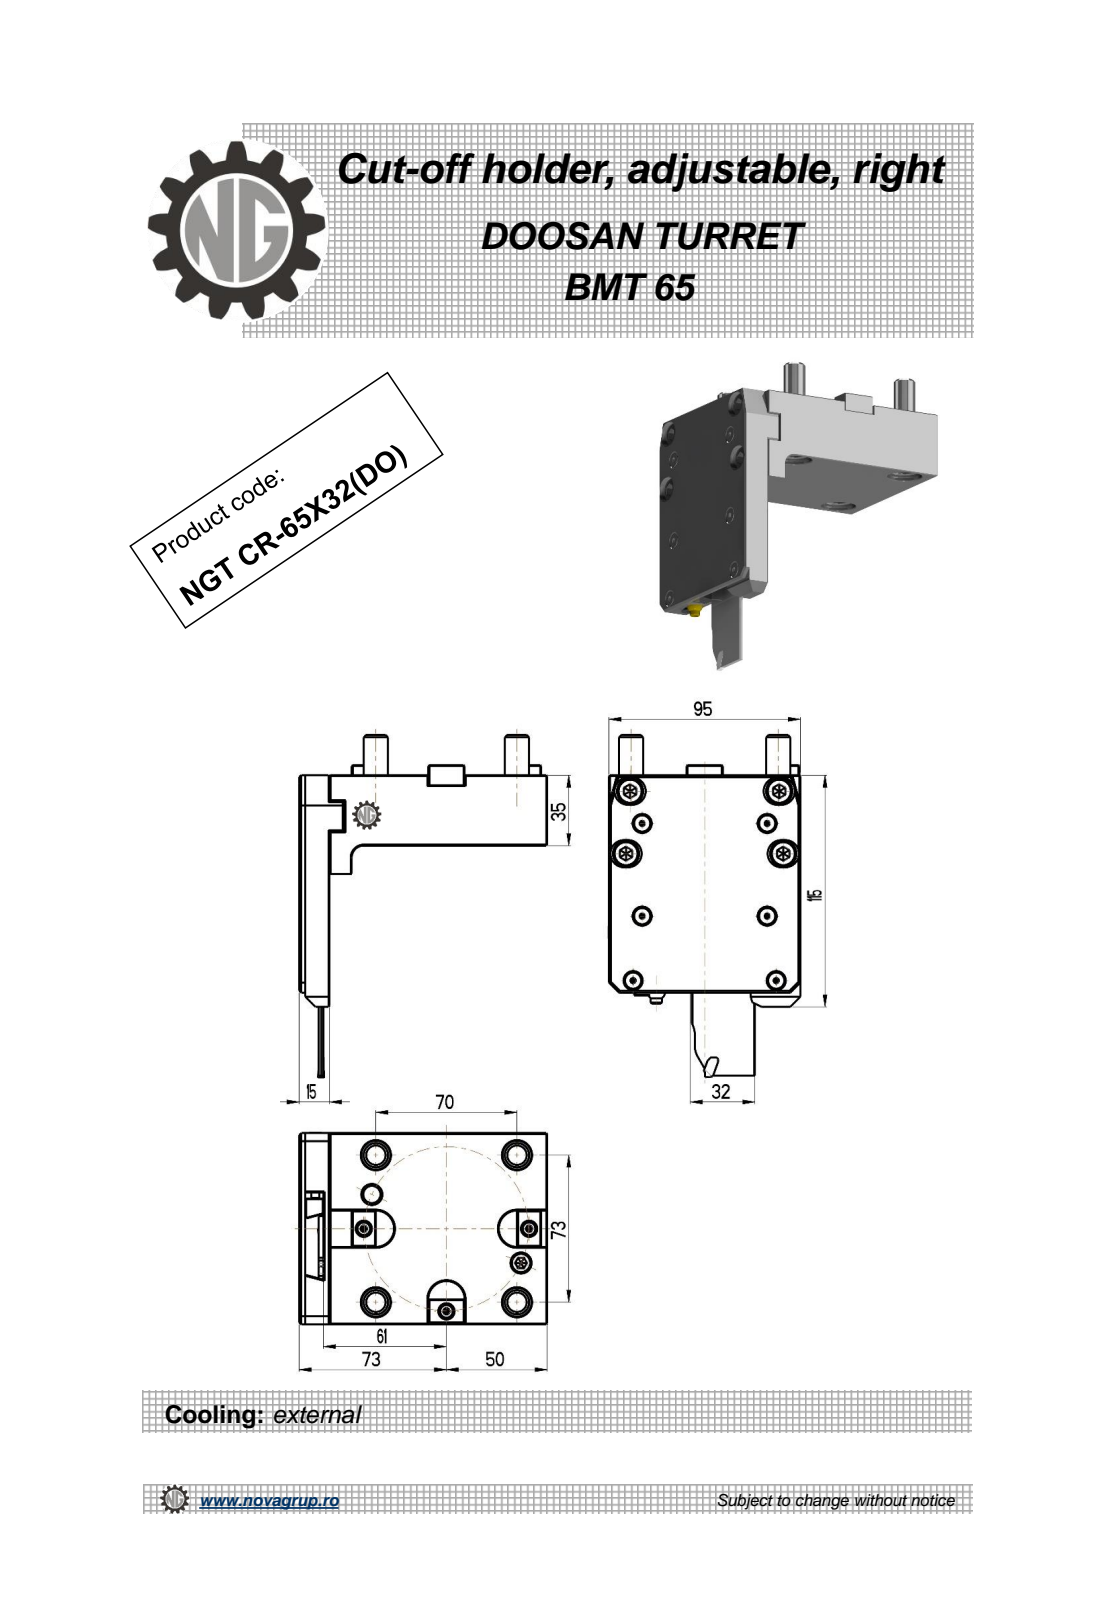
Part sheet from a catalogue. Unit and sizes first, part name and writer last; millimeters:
Units: millimetres
Overall size (bounding box): 135 × 123 × 95.13
Round holes (diameter × count): ⌀8 ×4, ⌀5 ×3, ⌀6.8 ×2, ⌀3.5 ×1, ⌀4.5 ×1, ⌀8.5 ×1, ⌀9 ×1
Round bosses / shafts (diameter × count): ⌀13 ×4, ⌀12 ×4, ⌀4 ×4, ⌀6 ×2, ⌀8 ×1, ⌀7 ×1, ⌀5.5 ×1
Partial cylindrical surfaces — rounded edges, fillets, slot ends (radius × count): R0.26 ×24, R0.31 ×12, R6.75 ×8, R0.14 ×6, R0.16 ×6, R0.51 ×6, R9 ×3, R6 ×1
Main face-to-face distances: 12, 3, 35, 15, 95, 9, 108, 120, 111, 123
Hole centre spacings: 17, 25.93, 27.41, 34, 64.67, 78
Volume: 479 361 mm³ · Surface area: 84 340 mm²
Bodies: 1 solid, 559 faces (321 planar, 135 cylindrical, 103 other)
Part name (STEP PRODUCT): NGT_CR_65_32_DO
STEP written by: PRO/ENGINEER BY PARAMETRIC TECHNOLOGY CORPORATION, 2010280 (CONFIG_CONTROL_DESIGN)
